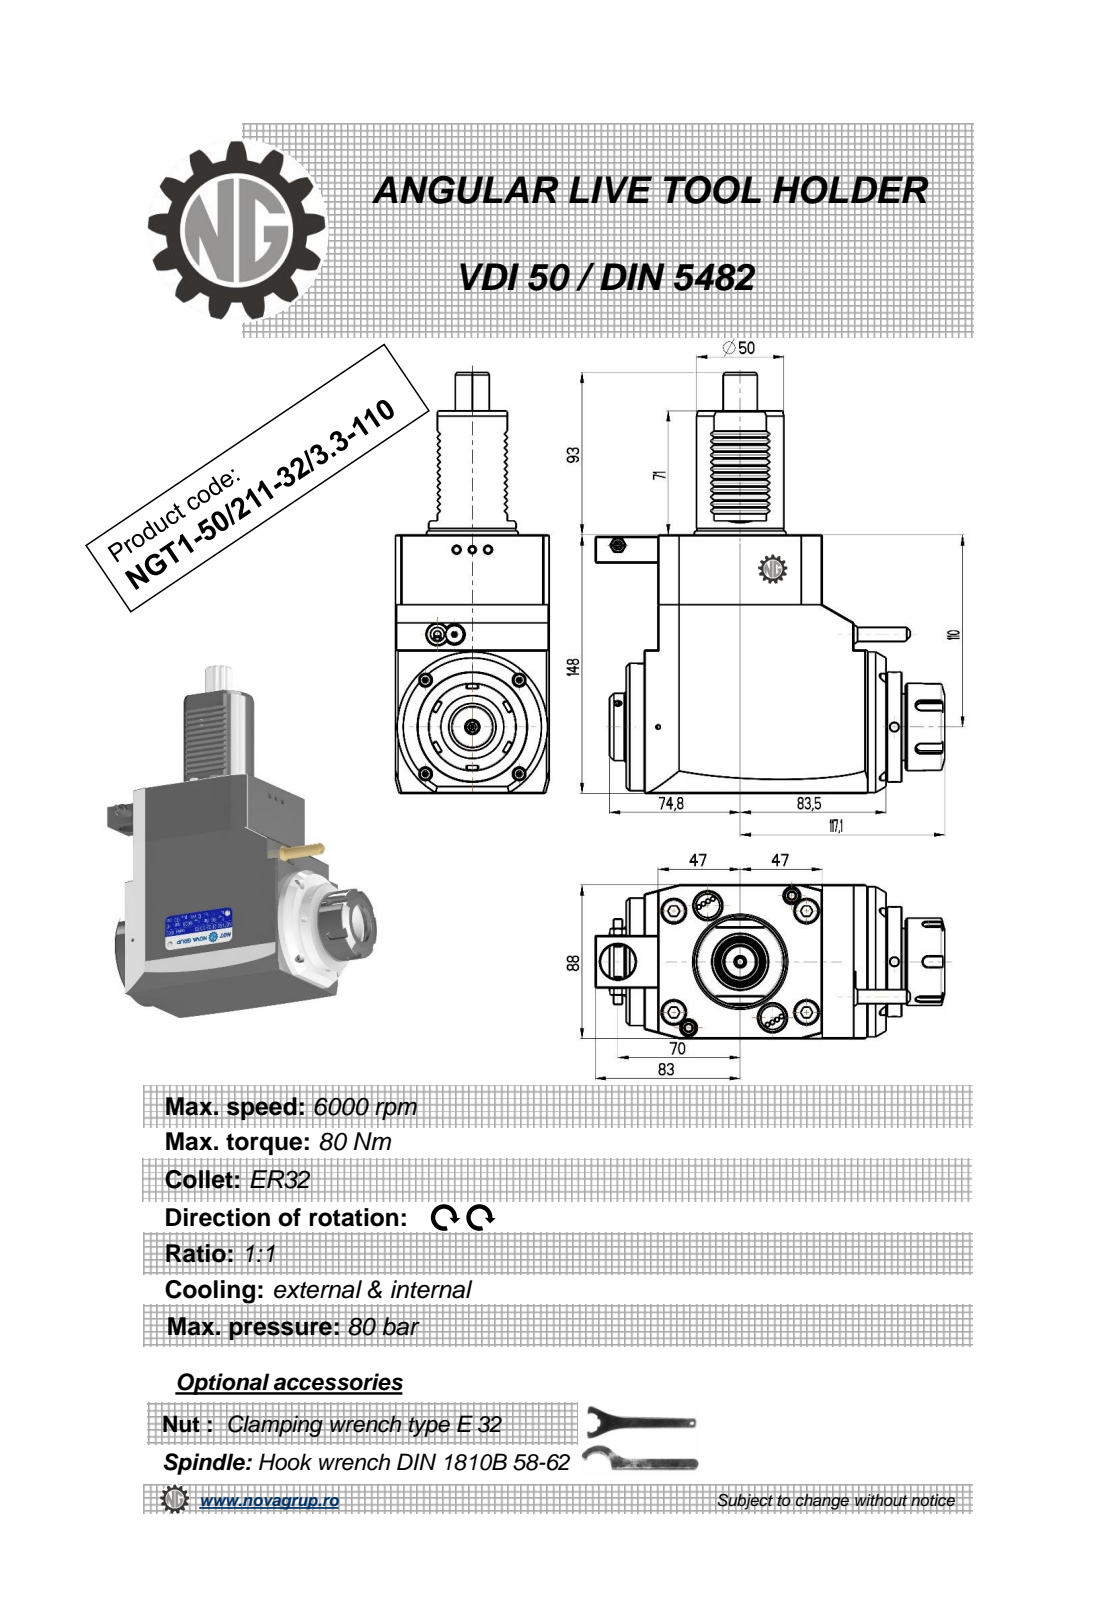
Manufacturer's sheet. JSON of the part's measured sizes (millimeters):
{"part_name": "NGT1_50_211_32_3_3_110", "step_written_by": "PRO/ENGINEER BY PARAMETRIC TECHNOLOGY CORPORATION, 2010280 (CONFIG_CONTROL_DESIGN)", "units": "millimeters", "bodies": {"solids": 1, "faces": 536, "planar": 231, "cylindrical": 154, "other": 151}, "overall_size": [241, 200.1, 88], "volume_mm3": 1807000, "surface_area_mm2": 114083, "round_holes": [[5, 3], [3, 1], [4.2, 1], [5.3, 1], [9.5, 1], [20, 1], [27, 1]], "round_bosses_or_shafts": [[50, 2], [86, 1], [73, 1], [63, 1], [41, 1], [38.5, 1], [10, 1], [8.96, 1]], "partial_cylinders_radius": [[0.3, 24], [3.33, 24], [0.26, 12], [0.2, 6], [3, 5], [8.25, 1], [9.75, 1]], "face_to_face_distances": [88, 148, 8, 94, 130.5, 36.5, 120, 18.3, 112.3, 148.8], "hole_center_spacings": [52.46, 56.65, 70, 88.25, 101.5, 158.25]}
